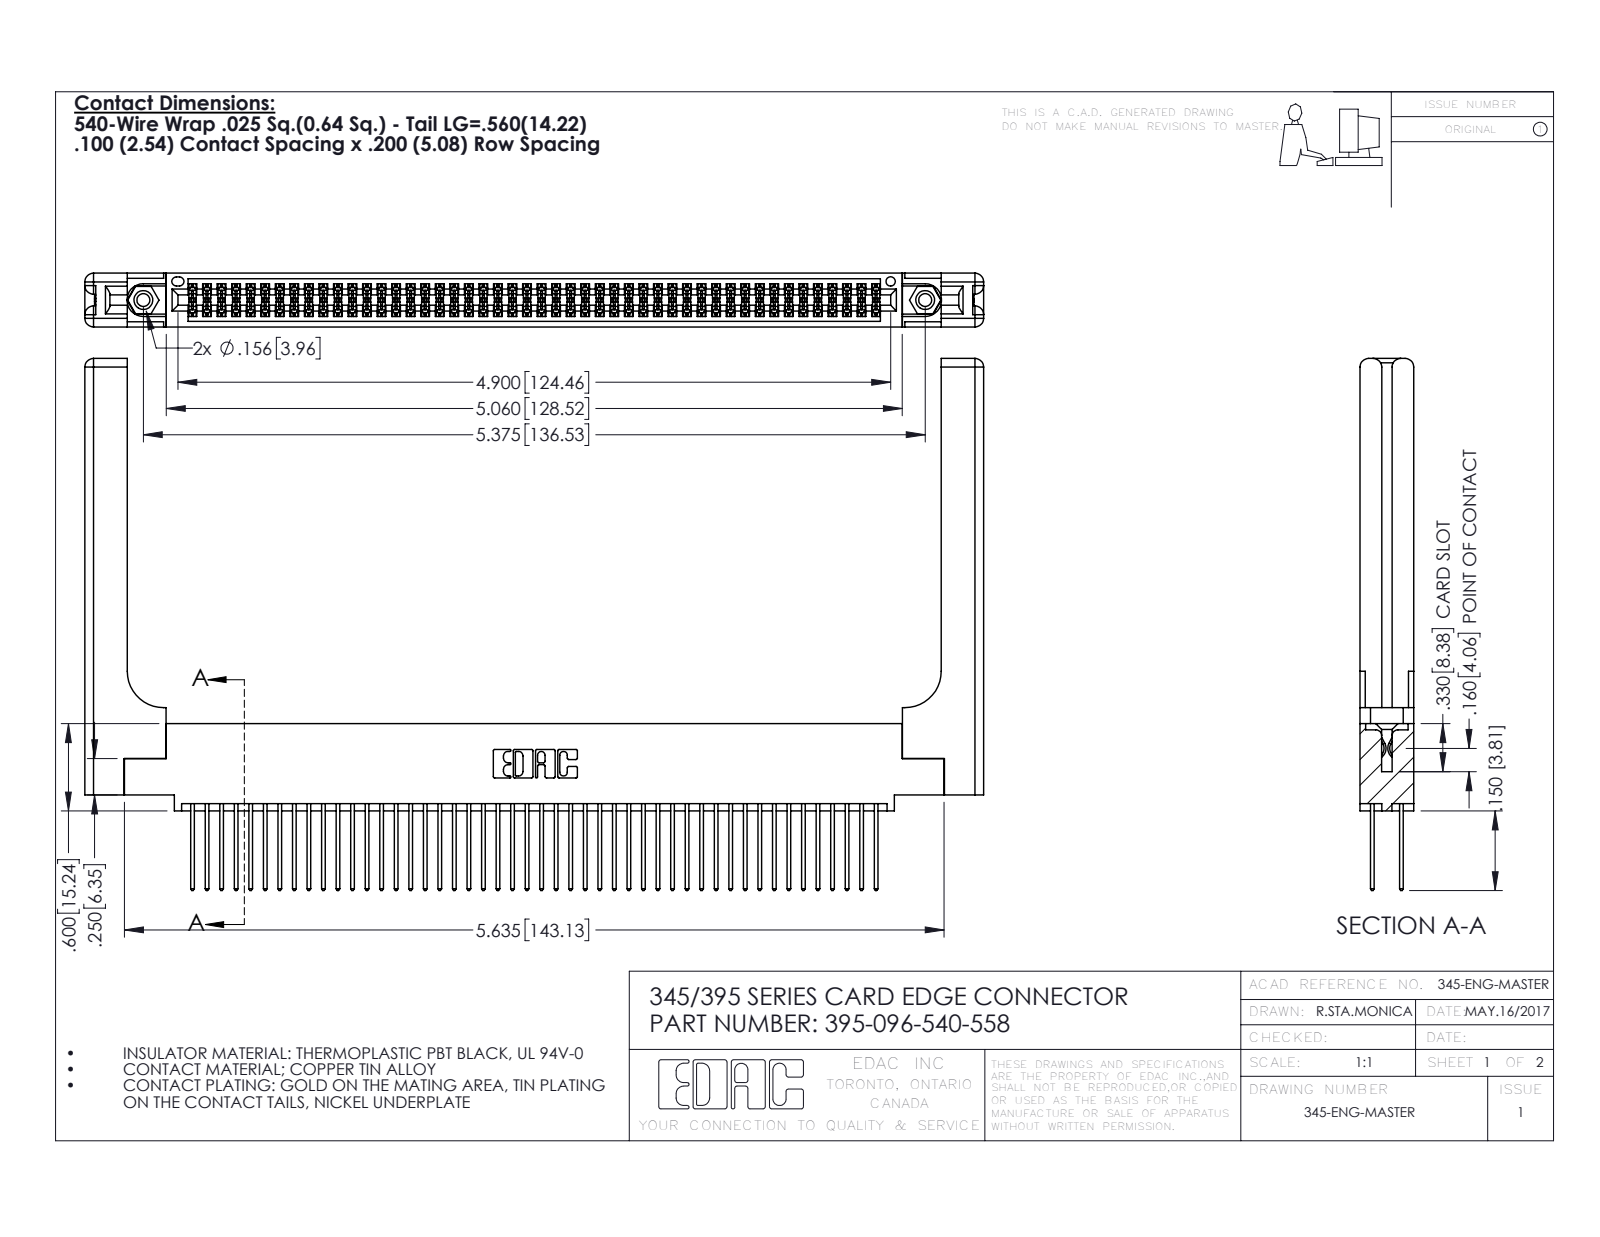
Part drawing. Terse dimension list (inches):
name: 345-292-001_345-293-140; 345 Part_0.110 Offset - 0.156 Dia-TH; 345-250-001_345-250-001-102; 345-220-058_345-220-058 (+1 more)
written by: SolidWorks 2016 (CONFIG_CONTROL_DESIGN)
unit: in
bodies: 101 solids, 5186 faces (3400 planar, 1726 cylindrical, 60 other)
size: 6.179 × 3.657 × 0.37
volume: 1.469 in³; area: 46.51 in²
holes: 2× ⌀0.089, 2× ⌀0.125, 2× ⌀0.156, 1× ⌀0.064
bosses: 2× ⌀0.155
rounds: 144× R0.006, 96× R0.01, 22× R0.01, 16× R0.06, 6× R0.007, 6× R0.031, 3× R0.026, 2× R0.014
face distances: 0.072, 0.298, 0.37, 0.098, 0.272, 0.025, 0.2, 0.225, 0.175, 0.148
hole spacings: 0.27, 5.139, 5.375
